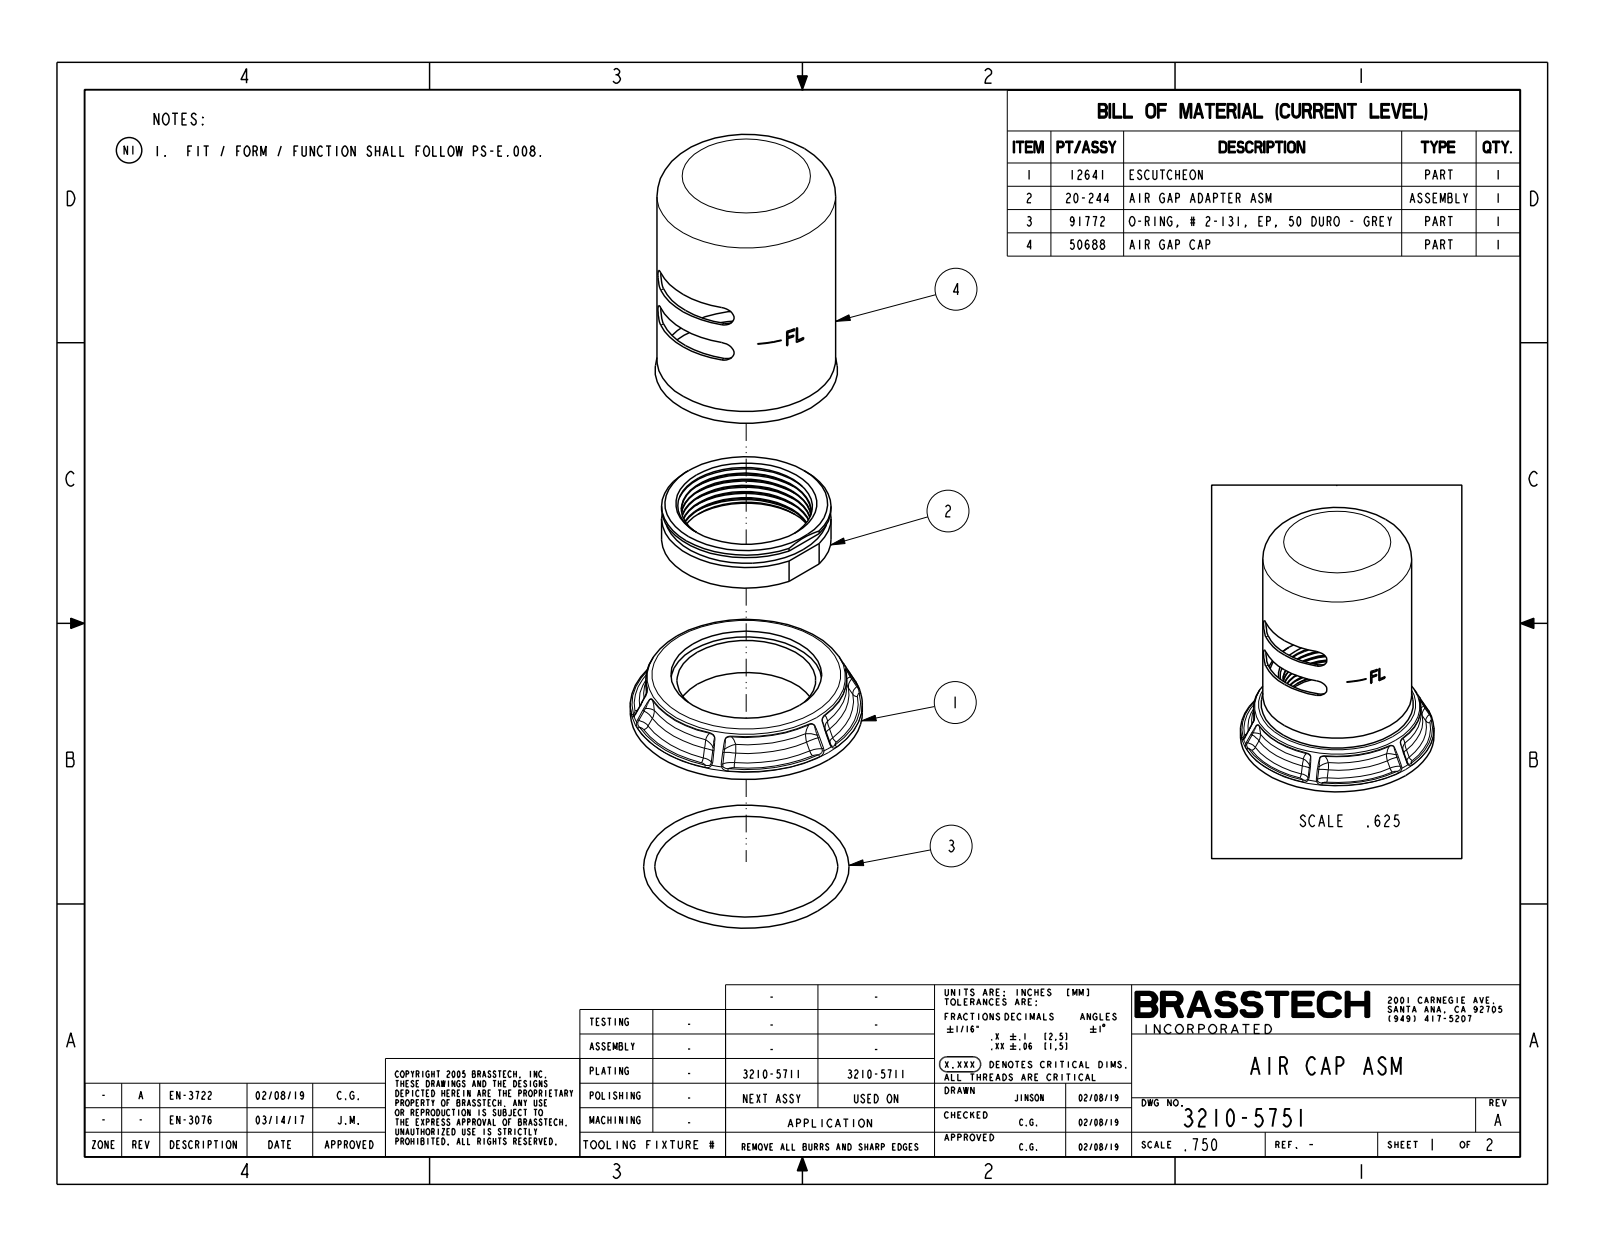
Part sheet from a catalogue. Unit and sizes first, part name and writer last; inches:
Units: inches
Overall size (bounding box): 2.615 × 2.343 × 2.146
Round holes (diameter × count): ⌀1.19 ×1, ⌀1.27 ×1, ⌀1.38 ×1, ⌀1.575 ×1, ⌀1.925 ×1
Round bosses / shafts (diameter × count): ⌀2.125 ×1, ⌀1.84 ×1, ⌀1.685 ×1, ⌀1.635 ×1, ⌀1.55 ×1, ⌀1.39 ×1, ⌀1.36 ×1
Partial cylindrical surfaces — rounded edges, fillets, slot ends (radius × count): R0.098 ×4, R0.808 ×1, R1.282 ×1
Main face-to-face distances: 2.19, 0.425, 2.615, 2.585, 2.16, 0.03, 0.085, 0.34, 2.5, 2.53
Volume: 1.291 in³ · Surface area: 65.12 in²
Bodies: 4 solids, 437 faces (58 planar, 58 cylindrical, 321 other)
Part name (STEP PRODUCT): 12641; 12736; 91227; 20-244_ASM (+2 more)
STEP written by: PRO/ENGINEER BY PARAMETRIC TECHNOLOGY CORPORATION, 2013150 (CONFIG_CONTROL_DESIGN)
